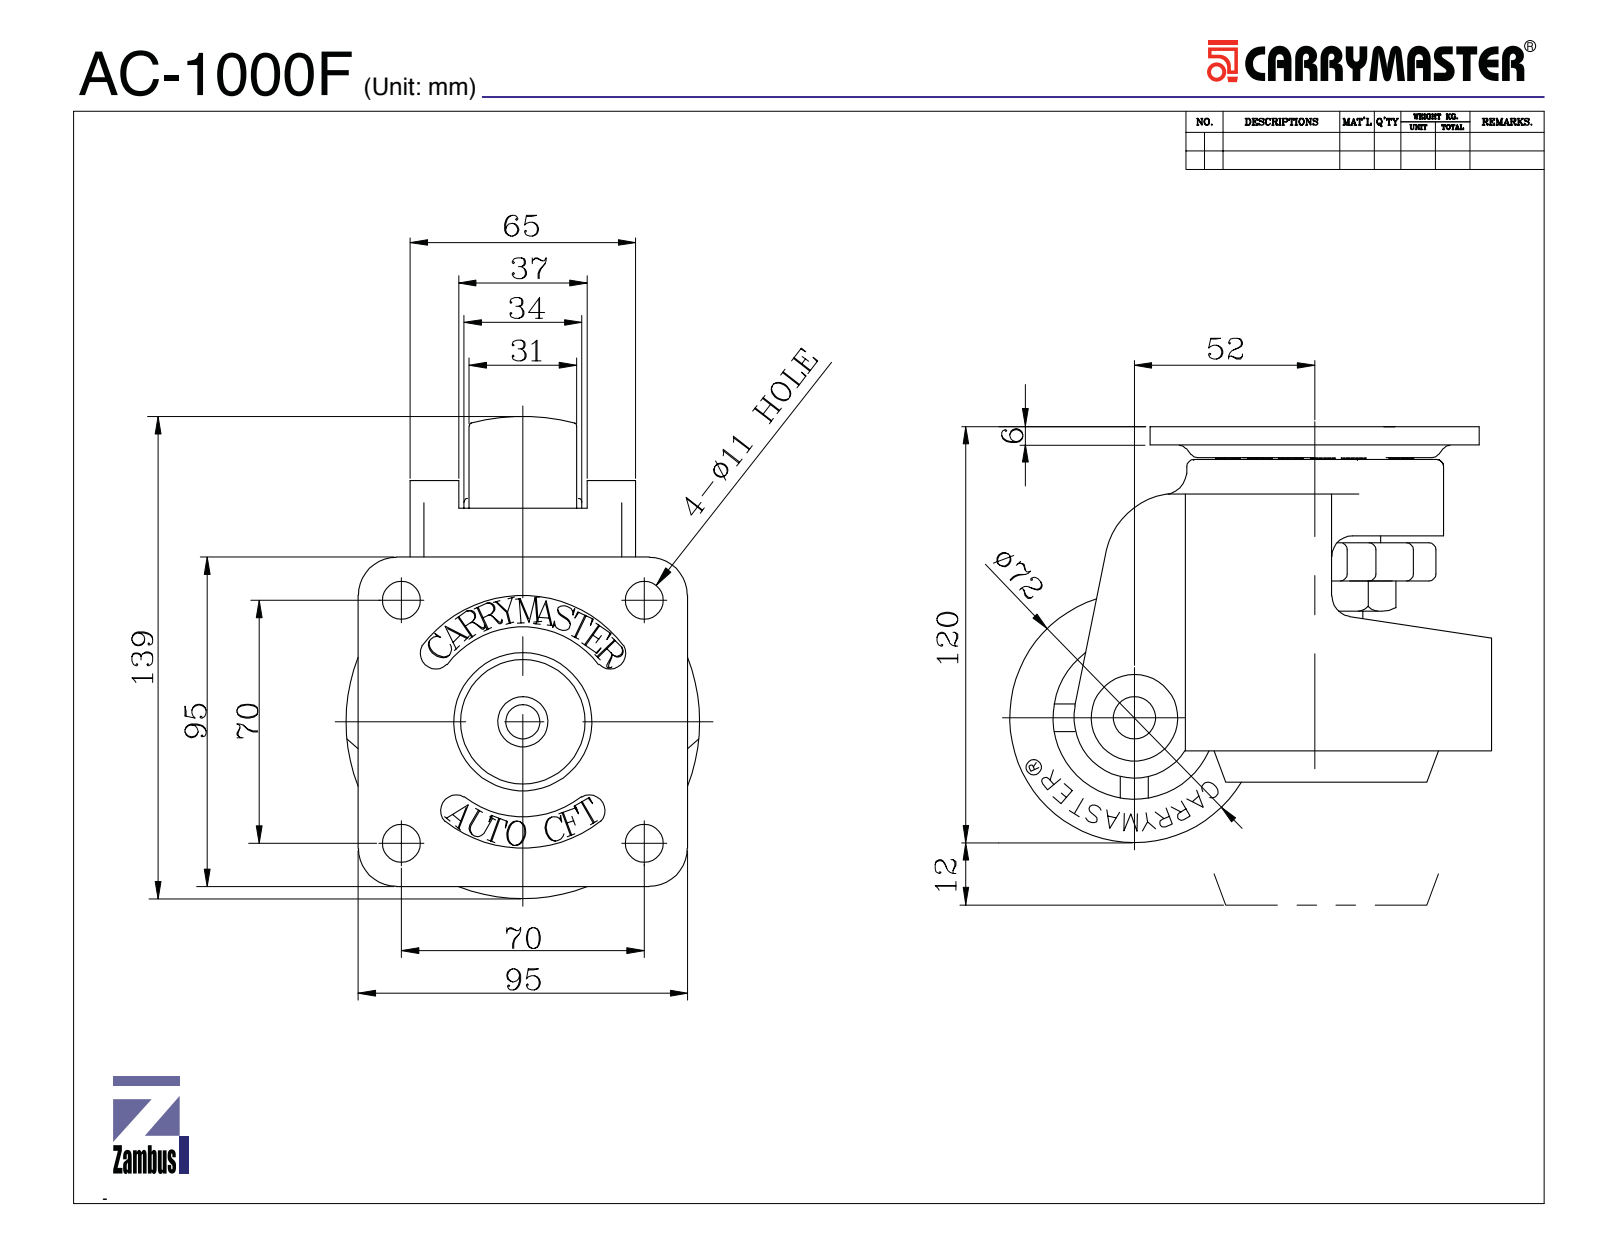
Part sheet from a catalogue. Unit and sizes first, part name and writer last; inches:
Units: inches
Overall size (bounding box): 5.472 × 4.759 × 4.094
Round holes (diameter × count): ⌀0.433 ×4, ⌀0.098 ×1, ⌀0.268 ×1, ⌀0.394 ×1, ⌀0.402 ×1, ⌀0.48 ×1, ⌀0.512 ×1, ⌀0.531 ×1, ⌀0.689 ×1, ⌀1.063 ×1, ⌀1.181 ×1, ⌀1.594 ×1
Round bosses / shafts (diameter × count): ⌀0.984 ×2, ⌀0.472 ×2, ⌀4.016 ×1, ⌀2.913 ×1, ⌀1.496 ×1, ⌀1.102 ×1, ⌀0.866 ×1, ⌀0.787 ×1
Partial cylindrical surfaces — rounded edges, fillets, slot ends (radius × count): R0.039 ×24, R0.079 ×16, R0.315 ×8, R0.118 ×6, R0.059 ×4, R0.433 ×4, R0.236 ×2, R0.217 ×1
Main face-to-face distances: 0.472, 1.398, 0.591, 0.236, 2.933, 3.169, 1.142, 0.787, 1.535, 1.894
Hole centre spacings: 1.949, 2.756, 3.897
Volume: 38.58 in³ · Surface area: 256.4 in²
Bodies: 31 solids, 1650 faces (769 planar, 281 cylindrical, 600 other)
Part name (STEP PRODUCT): AC-1000F ASSY
STEP written by: SolidWorks 2015 (CONFIG_CONTROL_DESIGN)
